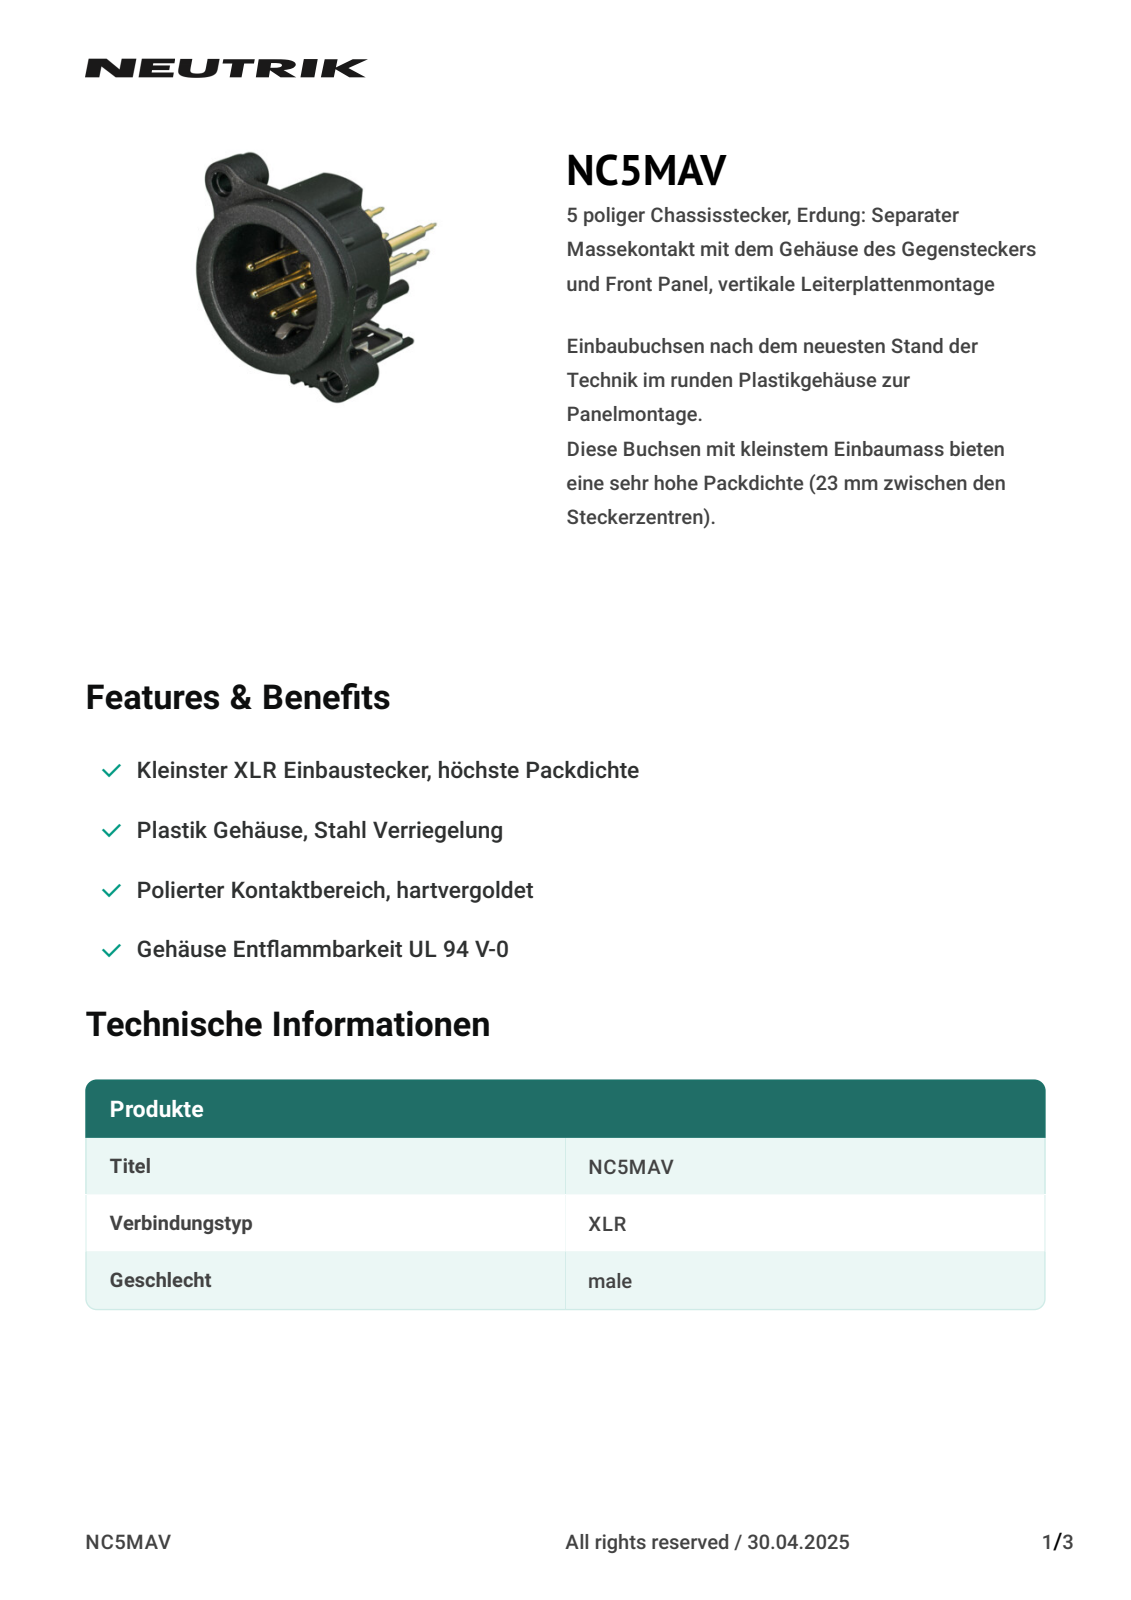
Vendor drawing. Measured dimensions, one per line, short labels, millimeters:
name: NC5MAV
written by: CREO PARAMETRIC BY PTC INC, 2019080 (CONFIG_CONTROL_DESIGN)
unit: mm
bodies: 1 solid, 1336 faces (499 planar, 265 cylindrical, 572 other)
size: 30.2 × 26.8 × 25.3
volume: 2 575 mm³; area: 5 058 mm²
holes: 5× ⌀1.8, 5× ⌀2.45, 1× ⌀2.3, 1× ⌀2.4, 1× ⌀2.5, 1× ⌀3.2
bosses: 5× ⌀2.4, 5× ⌀1.7, 5× ⌀1.5, 5× ⌀1.27, 5× ⌀1, 2× ⌀2, 1× ⌀5.2, 1× ⌀3
rounds: 57× R0.2, 48× R0.3, 11× R0.5, 9× R0.12, 7× R0.4, 7× R1, 5× R0.75, 3× R0.45
face distances: 1, 13.4, 14.4, 0.5, 2.7, 10.7, 11.7, 1.35, 4.2, 1.5
hole spacings: 4.29, 3.64, 4.27, 14, 3.62, 4.13, 6.57, 6.6
